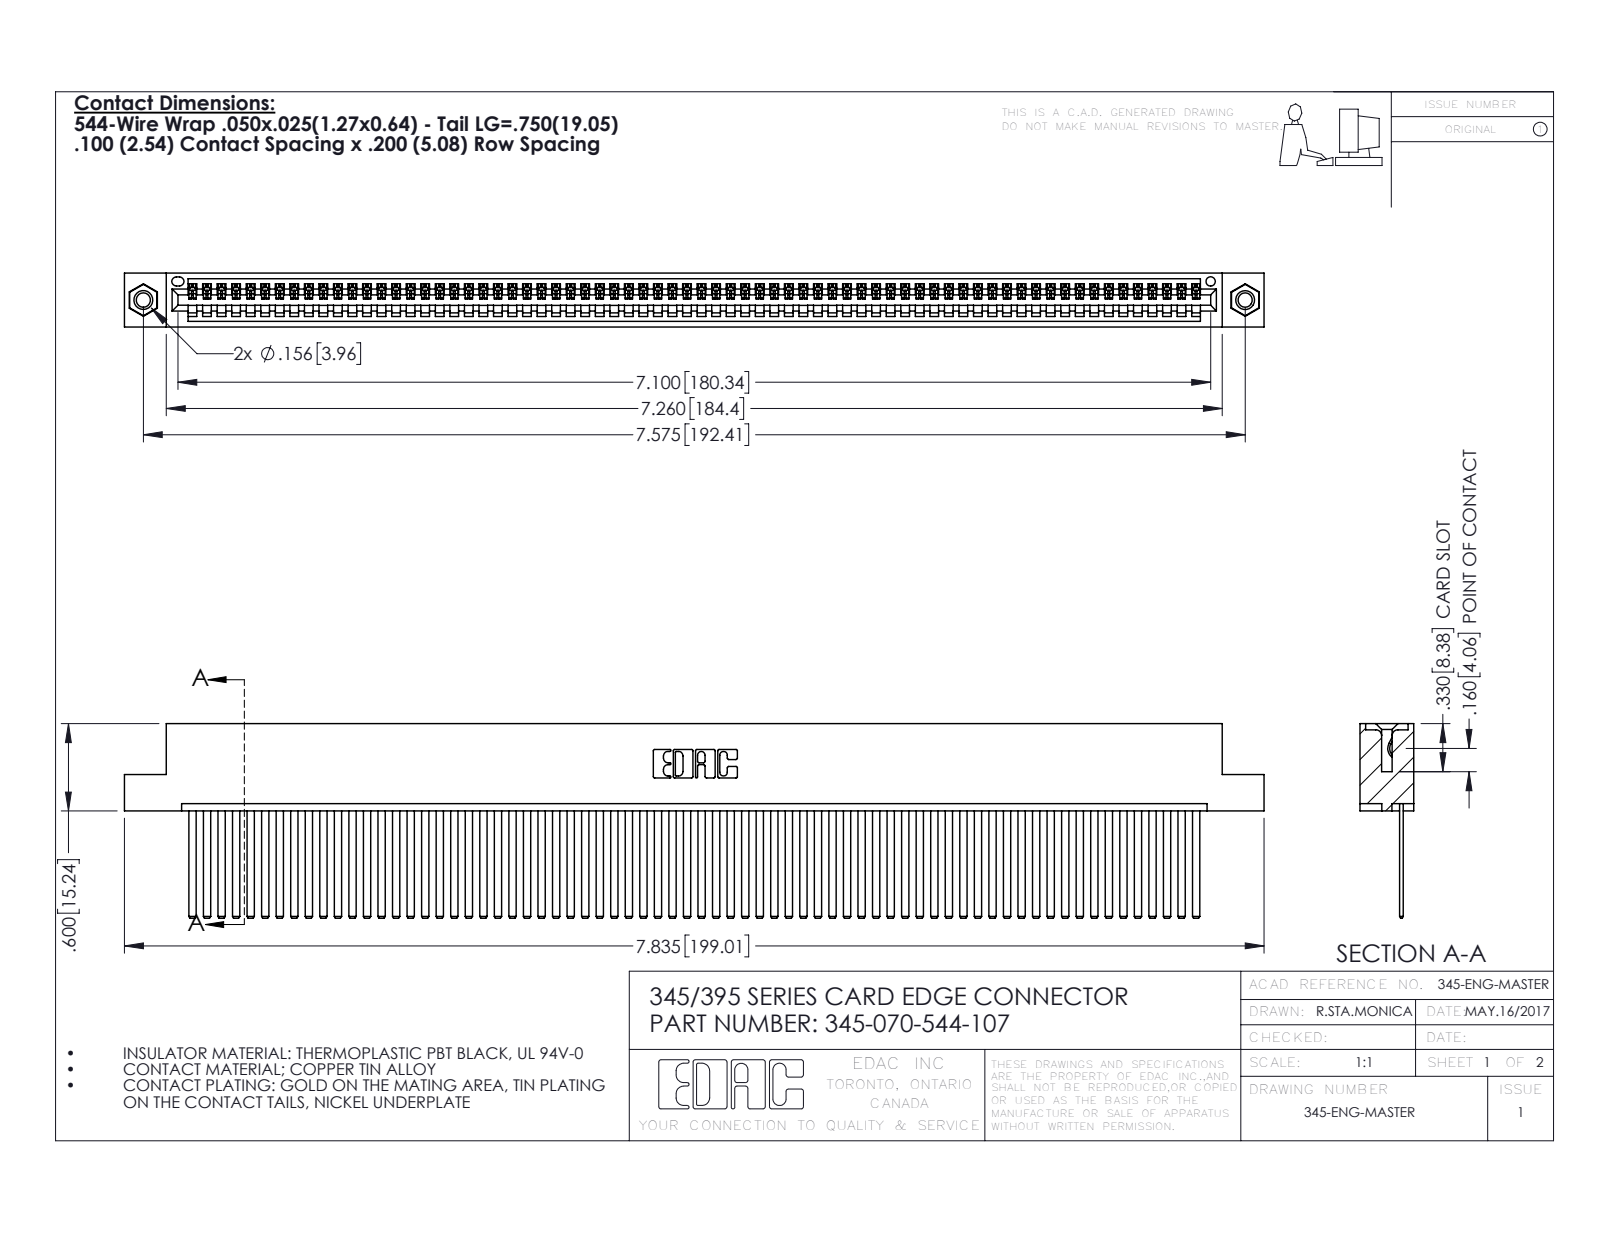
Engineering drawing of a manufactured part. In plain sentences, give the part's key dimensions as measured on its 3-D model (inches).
The part is named "345-070-544-107; 345-250-001_345-250-005-103; 345-292-001_345-293-144; 345 Part_Flush Mounting Lugs - 0.156 Dia-TI". Its 3-D file was written by "SolidWorks 2016 (CONFIG_CONTROL_DESIGN)". It is 73 solids with 3826 faces: 2632 planar, 1178 cylindrical and 16 other. Overall it measures 7.835 by 1.337 by 0.37 inches. Its volume is 1.216 cubic inches and its surface area 45.46 square inches. Round holes: 2 of diameter 0.098, 2 of diameter 0.125, 2 of diameter 0.156, 1 of diameter 0.064. Round bosses or shafts: 2 of diameter 0.155. Partial cylindrical surfaces (rounded edges, fillets, slot ends): 140 of radius 0.006, 22 of radius 0.01, 6 of radius 0.007, 6 of radius 0.031, 3 of radius 0.026, 2 of radius 0.031, 2 of radius 0.04, 1 of radius 0.014. The main face-to-face distances are 0.072, 0.298, 0.025, 0.098, 0.272, 0.37, 0.2, 0.225, 0.149, 0.072. The hole center spacings are 0.27, 7.339, 7.575.
